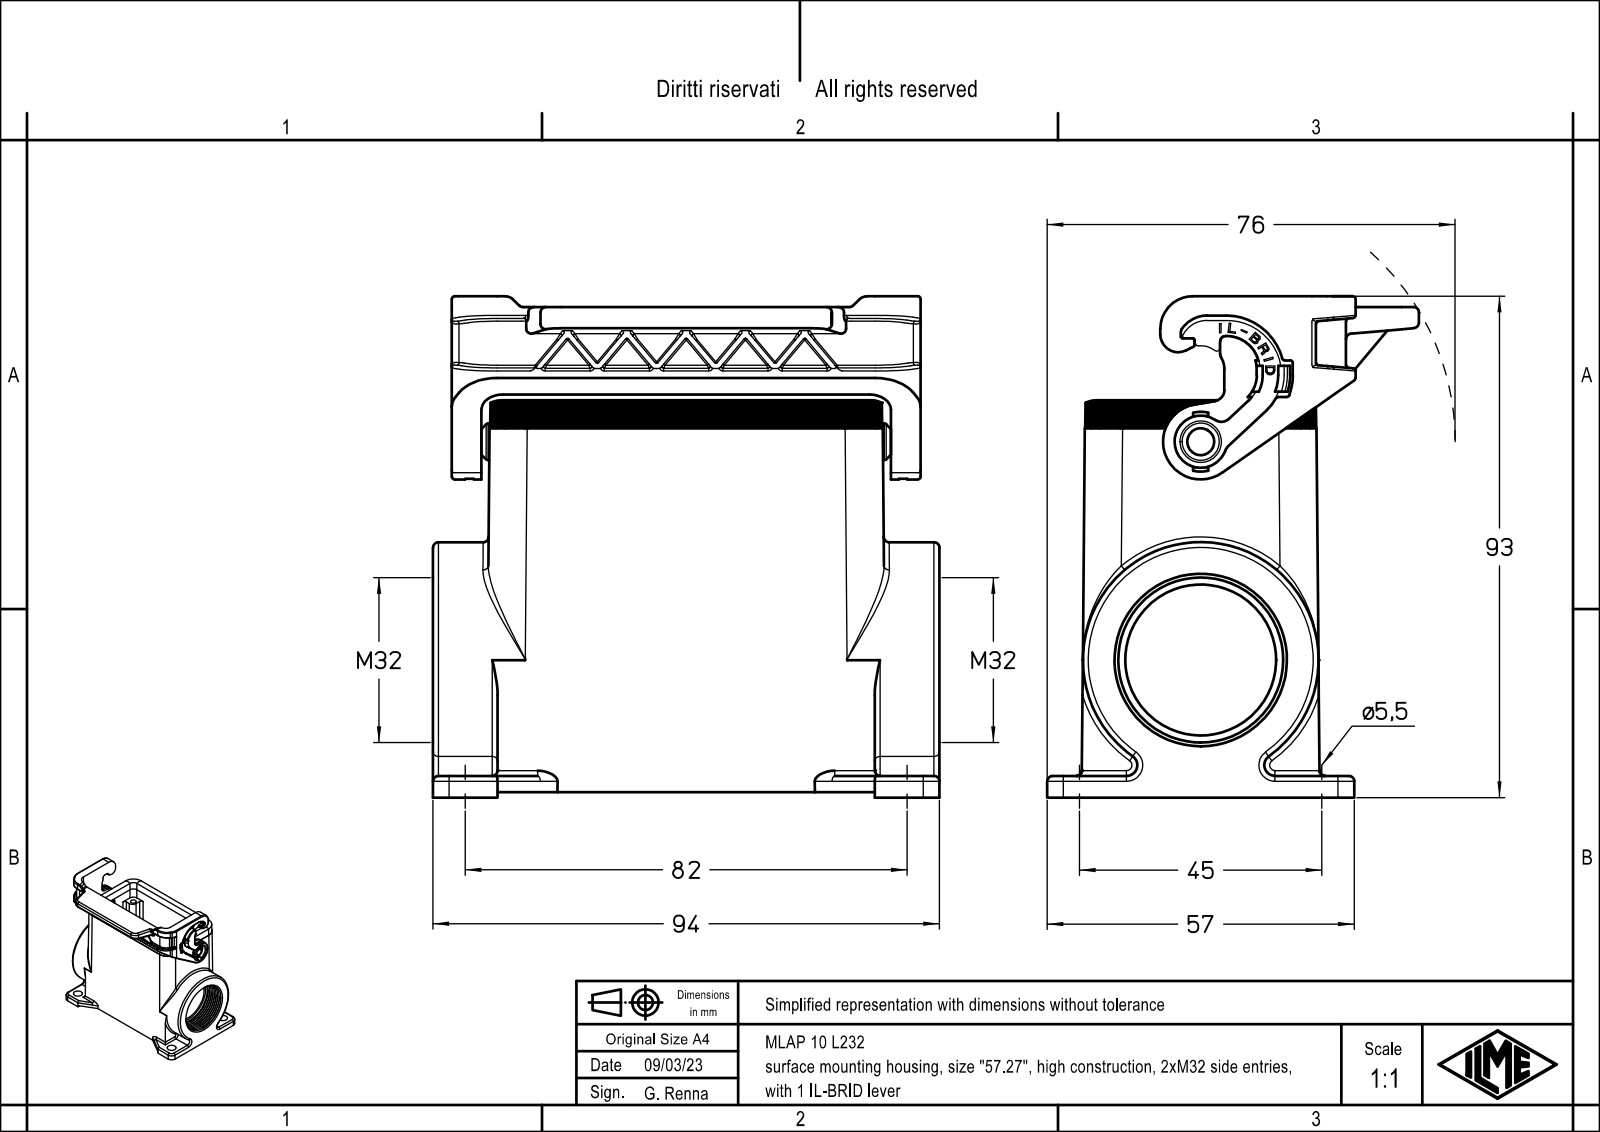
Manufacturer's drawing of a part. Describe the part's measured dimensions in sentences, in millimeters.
The part is named "MLAP 10 L32". Its 3-D file was written by "Creo Elements/Direct Modeling 20.1B 02-Apr-2019 (C) Parametric Technology GmbH (AUTOMOTIVE_DESIGN)". It is 1 solid with 1041 faces: 623 planar, 288 cylindrical and 130 other. Overall it measures 94 by 93 by 69 millimeters. Its volume is 119 368 cubic millimeters and its surface area 55 646 square millimeters. Round holes: 4 of diameter 3, 4 of diameter 3.5, 4 of diameter 5.5, 1 of diameter 3.25, 1 of diameter 5.4, 1 of diameter 7.7, 1 of diameter 28, 1 of diameter 30.6. Round bosses or shafts: 1 of diameter 43.75, 1 of diameter 6.9, 1 of diameter 6.8, 1 of diameter 5.2, 1 of diameter 3.2. Partial cylindrical surfaces (rounded edges, fillets, slot ends): 27 of radius 0.1, 16 of radius 3, 15 of radius 0.2, 14 of radius 1, 11 of radius 0.5, 11 of radius 2, 10 of radius 7, 9 of radius 1.5. The main face-to-face distances are 3, 87, 1, 4, 91, 94, 5.5, 81.5, 14, 80. The hole center spacings are 15.4, 38.11, 70.08, 78.27, 27, 45, 57, 63.07.
